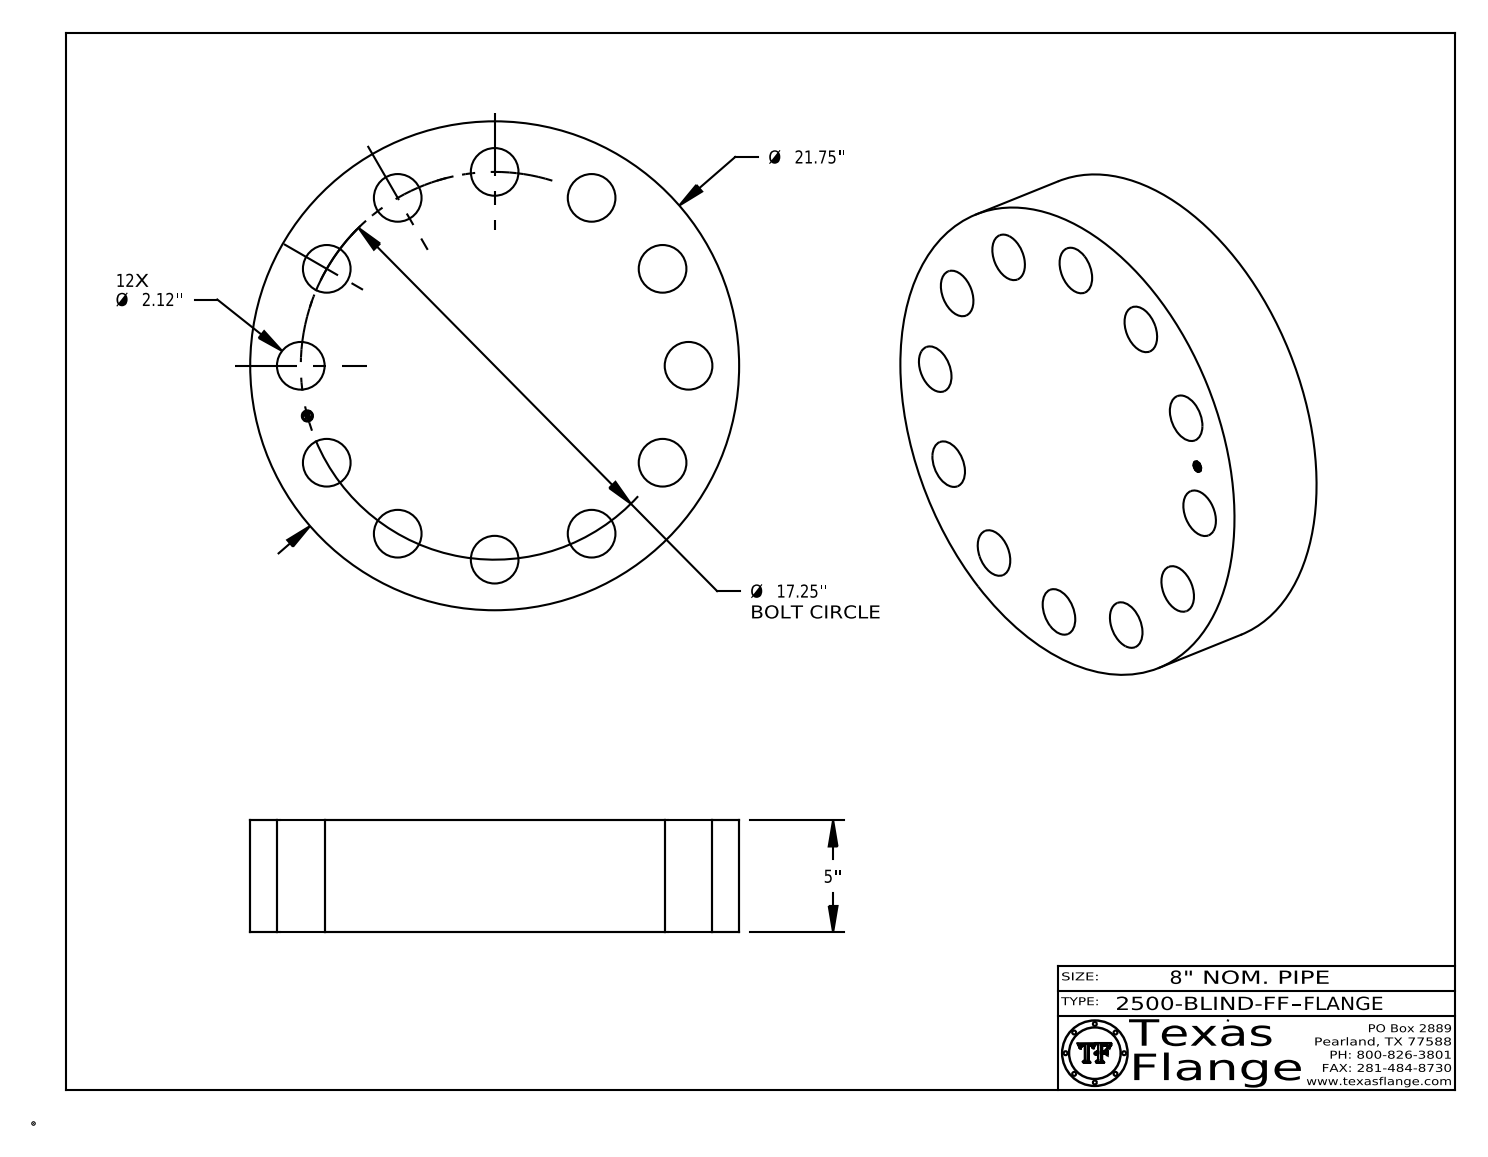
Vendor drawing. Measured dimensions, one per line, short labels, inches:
name: 2500-BLIND-FF
written by: CATIA V5 STEP AP214 (AUTOMOTIVE_DESIGN)
unit: in
bodies: 1 solid, 413 faces (367 planar, 46 cylindrical, 0 other)
size: 21.75 × 21.75 × 5
volume: 1 646 in³; area: 1 400 in²
holes: 12× ⌀2.12, 1× ⌀0.495
bosses: 8× ⌀0.03, 1× ⌀21.75, 1× ⌀0.39
face distances: 5, 4.985, 0.015, 0.148, 0.145, 0.027, 0.096, 0.122, 0.101, 0.022
hole spacings: 16.662, 4.465, 8.625, 12.198, 14.939, 4.464, 8.625, 12.198
